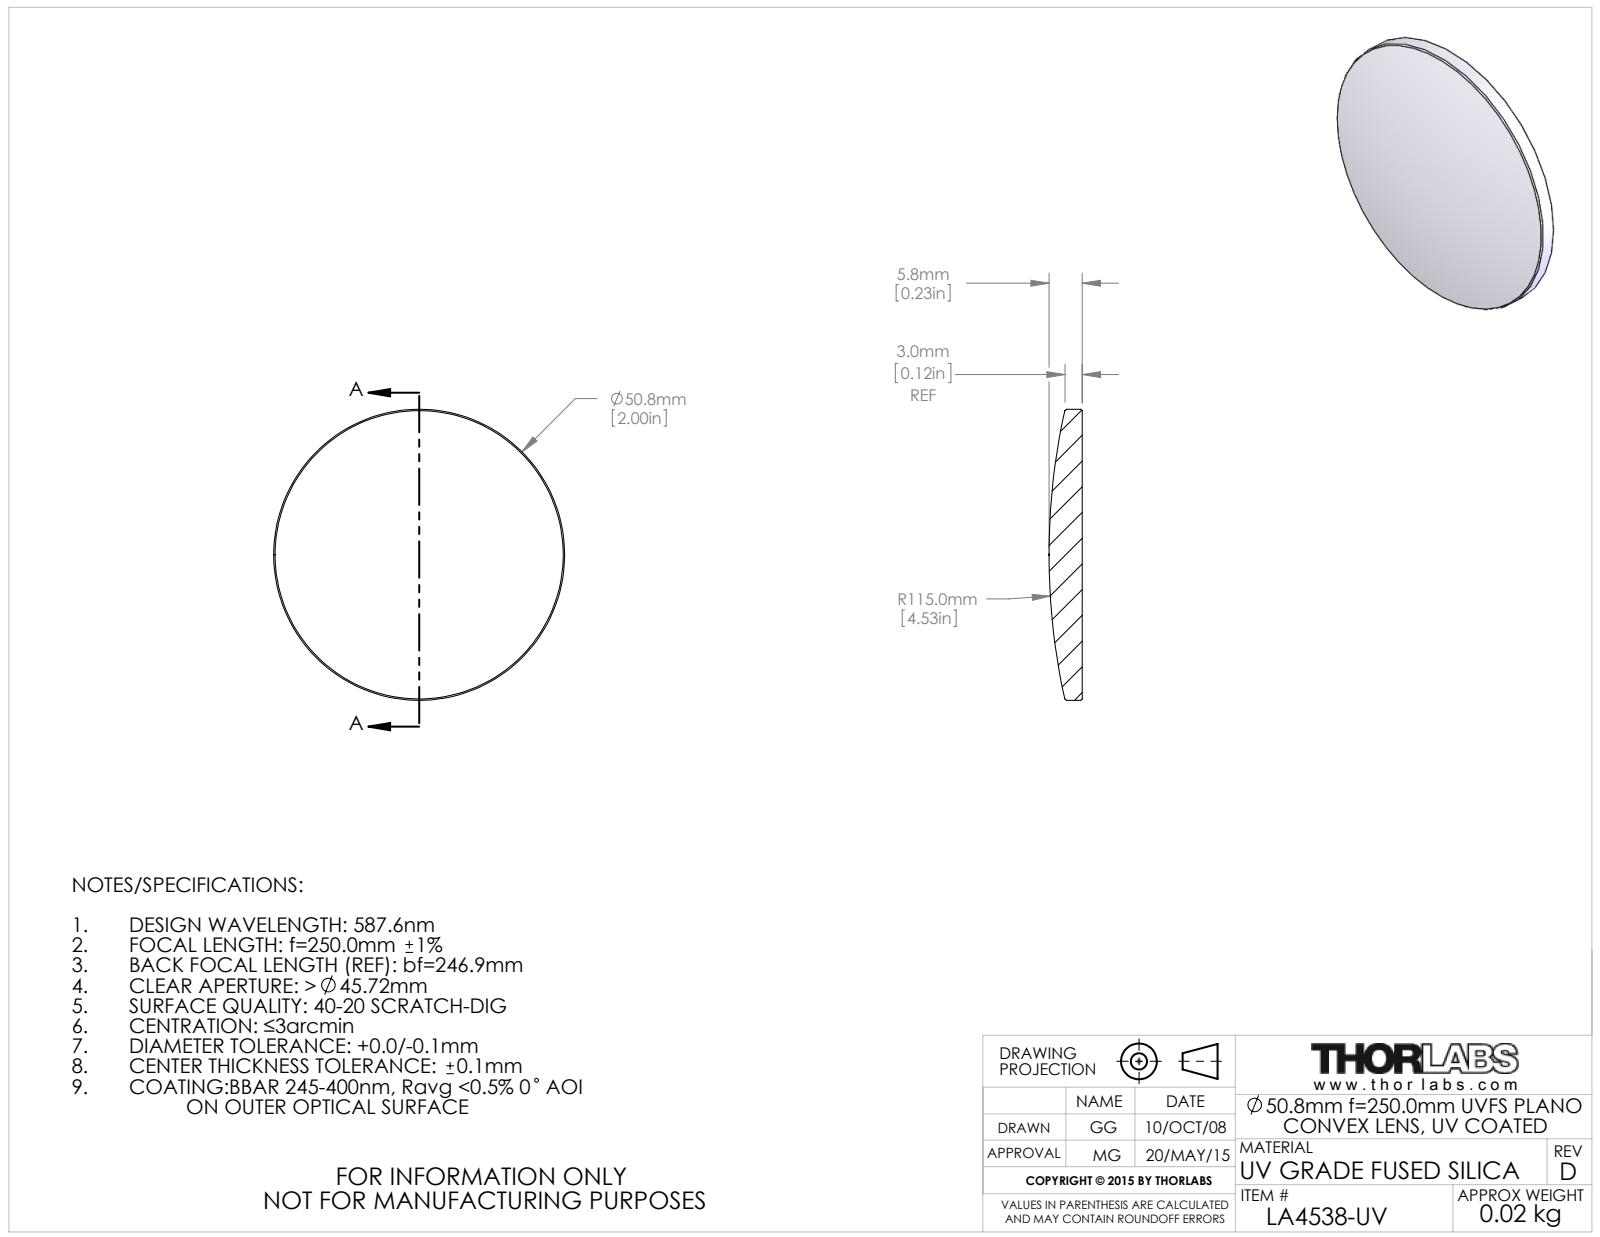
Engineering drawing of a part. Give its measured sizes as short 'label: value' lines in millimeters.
name: 4297-E0W
written by: SolidWorks 2014 (CONFIG_CONTROL_DESIGN)
unit: mm
bodies: 1 solid, 9 faces (1 planar, 2 cylindrical, 6 other)
size: 50.8 × 50.8 × 5.8
volume: 8 933 mm³; area: 4 516 mm²
bosses: 1× ⌀50.8
